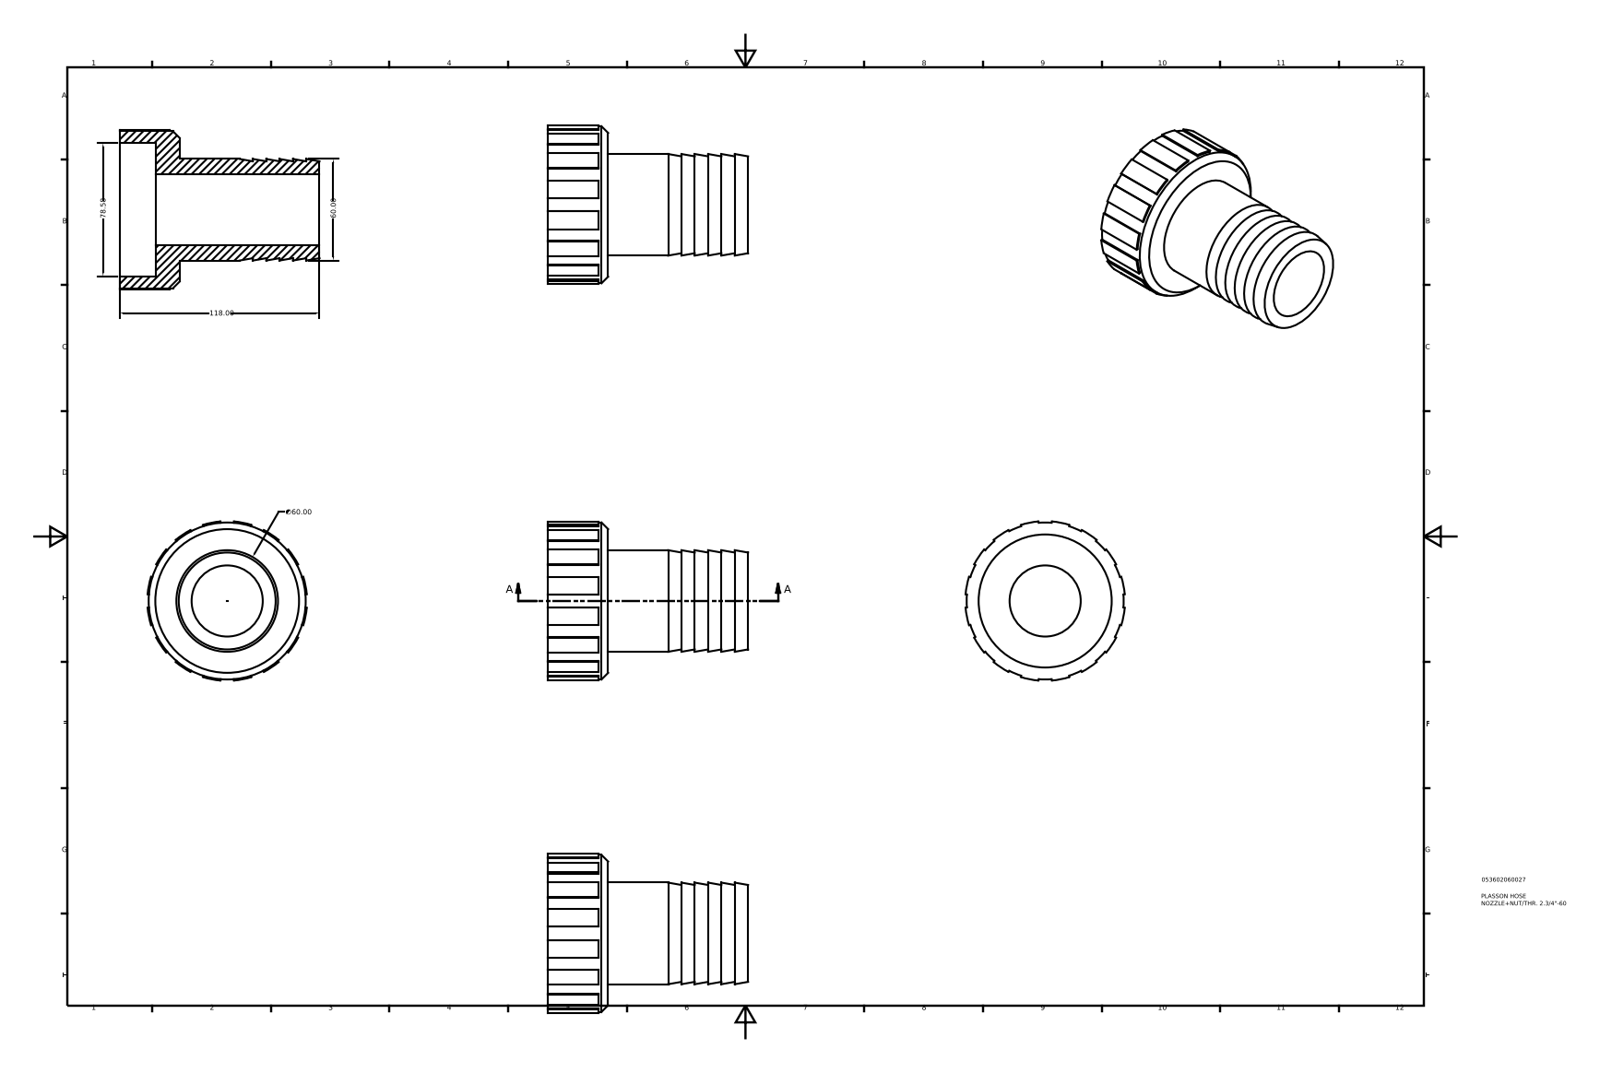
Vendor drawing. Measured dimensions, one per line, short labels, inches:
name: 053602060027
written by: Autodesk Inventor 2015 (AUTOMOTIVE_DESIGN)
unit: in
bodies: 1 solid, 84 faces (57 planar, 20 cylindrical, 7 other)
size: 4.646 × 3.699 × 3.699
volume: 14.11 in³; area: 86.76 in²
holes: 1× ⌀1.654, 1× ⌀3.094
bosses: 1× ⌀3.65, 1× ⌀2.362
rounds: 1× R1.856
face distances: 0.557, 0.836, 1.394, 4.646, 3.809, 3.252, 0.619, 0.929, 0.31, 0.309
